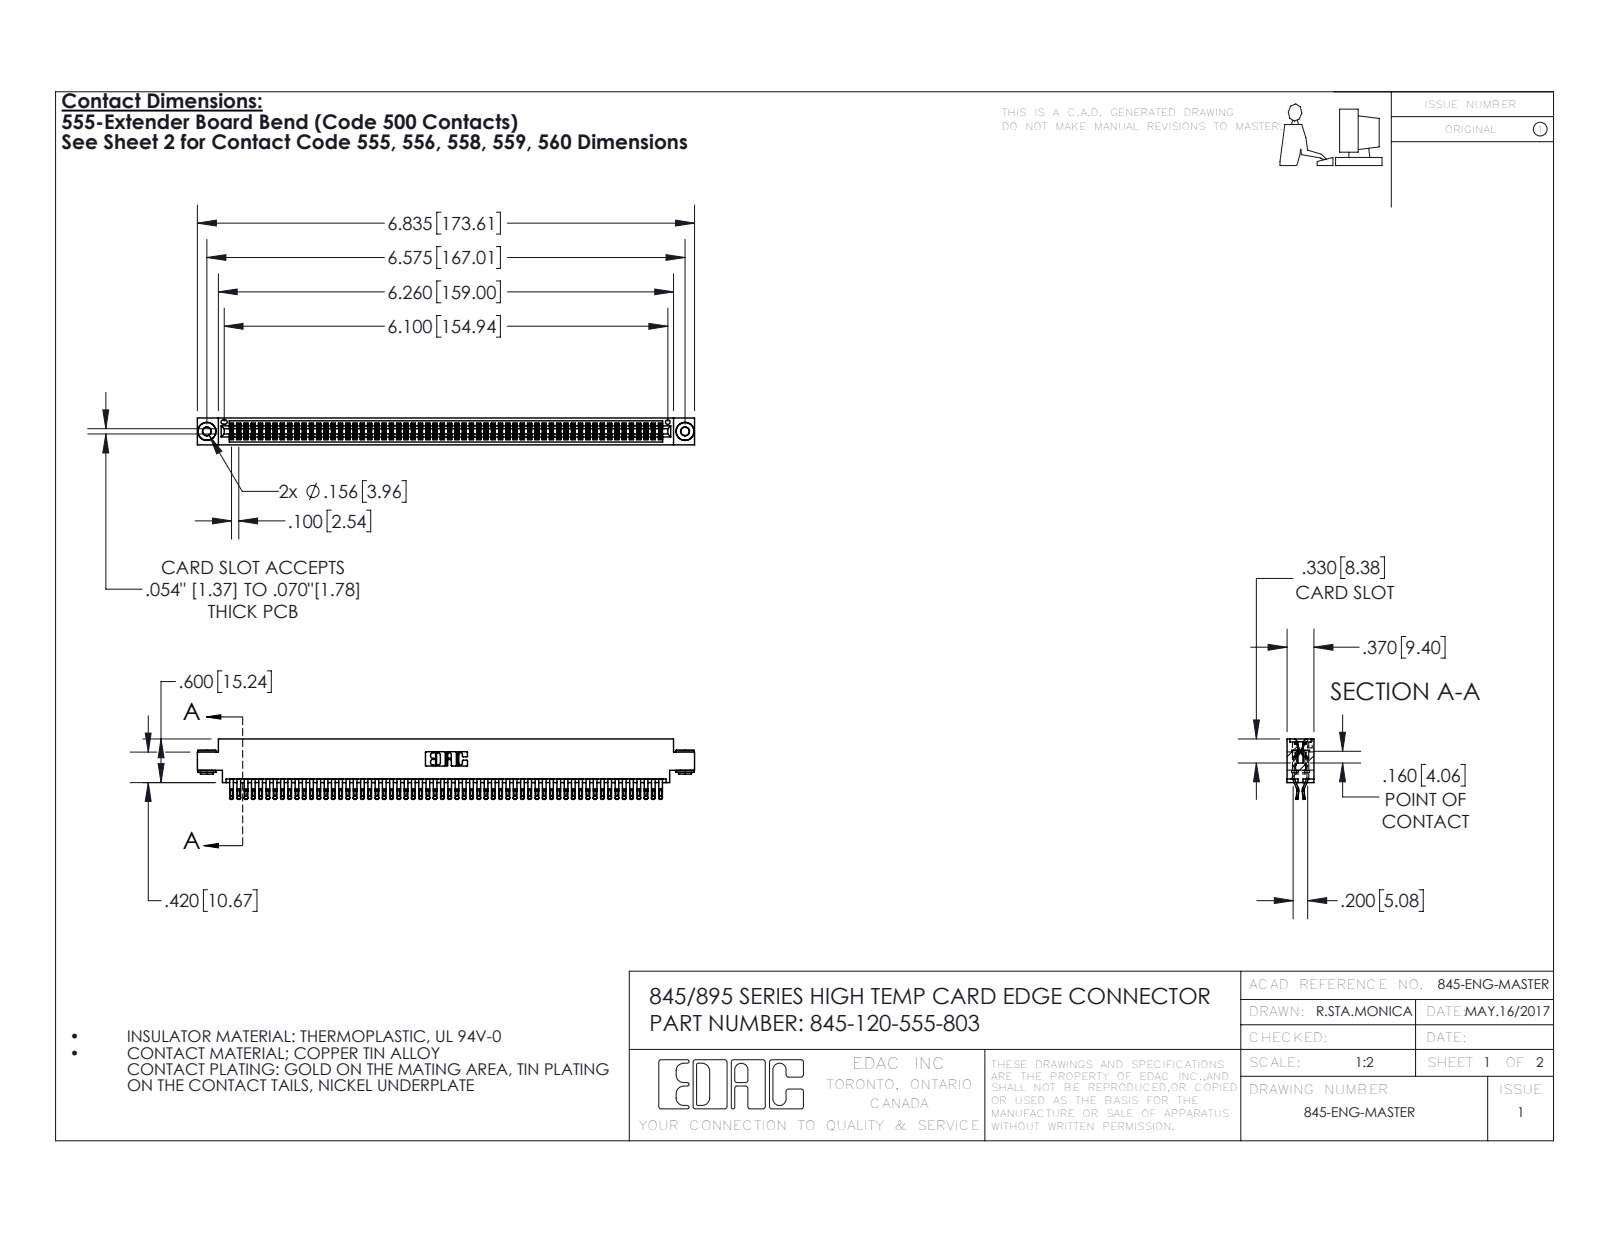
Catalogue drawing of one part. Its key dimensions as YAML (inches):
part_name: "345-292-001_555 Tail; 345-250-002_345-250-002-102; 845-120-555-803; 845 Part_0.170 Offset - 0.156 Dia-TH"
step_written_by: "SolidWorks 2016 (CONFIG_CONTROL_DESIGN)"
units: inches
bodies: {solids: 123, faces: 6888, planar: 3814, cylindrical: 3066, other: 8}
overall_size: [6.835, 0.832, 0.37]
volume: 1.055
surface_area: 42.56
round_holes:
  - {diameter: 0.116, count: 2}
  - {diameter: 0.156, count: 2}
  - {diameter: 0.064, count: 1}
round_bosses_or_shafts:
  - {diameter: 0.25, count: 2}
  - {diameter: 0.18, count: 2}
  - {diameter: 0.136, count: 2}
partial_cylinders:
  - {radius: 0.016, count: 300}
  - {radius: 0.02, count: 240}
  - {radius: 0.006, count: 180}
  - {radius: 0.01, count: 22}
  - {radius: 0.007, count: 6}
  - {radius: 0.031, count: 6}
  - {radius: 0.026, count: 3}
  - {radius: 0.01, count: 2}
face_to_face_distances: [0.072, 0.298, 0.37, 0.025, 0.2, 0.098, 0.272, 0.225, 0.175, 0.149]
hole_center_spacings: [0.27, 6.339, 6.575]
